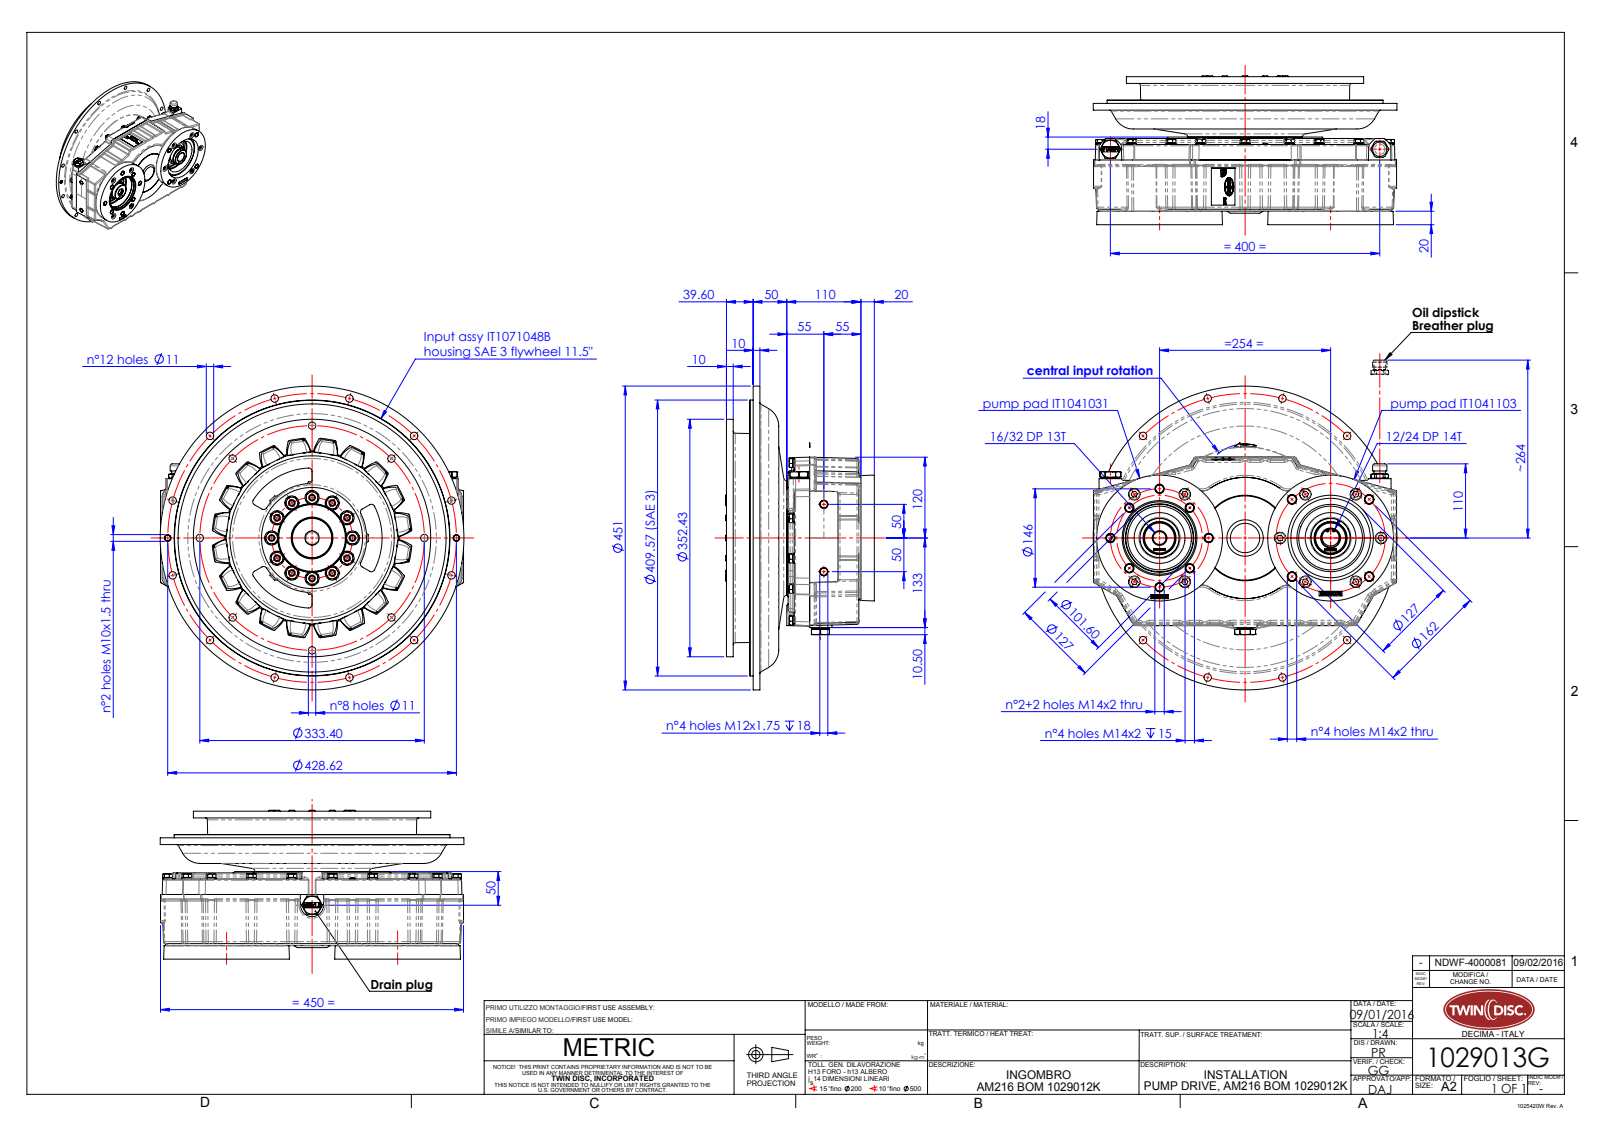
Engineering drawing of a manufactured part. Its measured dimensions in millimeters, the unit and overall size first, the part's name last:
Units: millimetres
Overall size (bounding box): 451 × 451 × 220.9
Round holes (diameter × count): ⌀10.5 ×22, ⌀11 ×22, ⌀8.2 ×19, ⌀8.8 ×19, ⌀9 ×19, ⌀12 ×14, ⌀17 ×10, ⌀10.2 ×8, ⌀10 ×4, ⌀14 ×4, ⌀8 ×3, ⌀18.5 ×3
Round bosses / shafts (diameter × count): ⌀10 ×32, ⌀16.2 ×20, ⌀14.8 ×19, ⌀12.2 ×19, ⌀8 ×19, ⌀21 ×12, ⌀16 ×10, ⌀18.1 ×8
Partial cylindrical surfaces — rounded edges, fillets, slot ends (radius × count): R3 ×106, R1 ×80, R4 ×80, R2.5 ×64, R0.25 ×46, R24.86 ×46, R42.91 ×40, R2 ×27
Main face-to-face distances: 130, 20, 54, 22, 76, 150, 108, 96, 23, 32.5
Hole centre spacings: 60, 75, 57.4, 91.02, 92.5, 106.06, 120, 138.58
Volume: 5 325 000 mm³ · Surface area: 2 111 000 mm²
Bodies: 32 solids, 6056 faces (2577 planar, 1579 cylindrical, 1900 other)
Part name (STEP PRODUCT): IT1041103_rev00-installation; IT1041031_rev00-installation; ITB00110000_rev01-installation; 1029013G (+4 more)
STEP written by: SolidWorks 2015 (AUTOMOTIVE_DESIGN)
